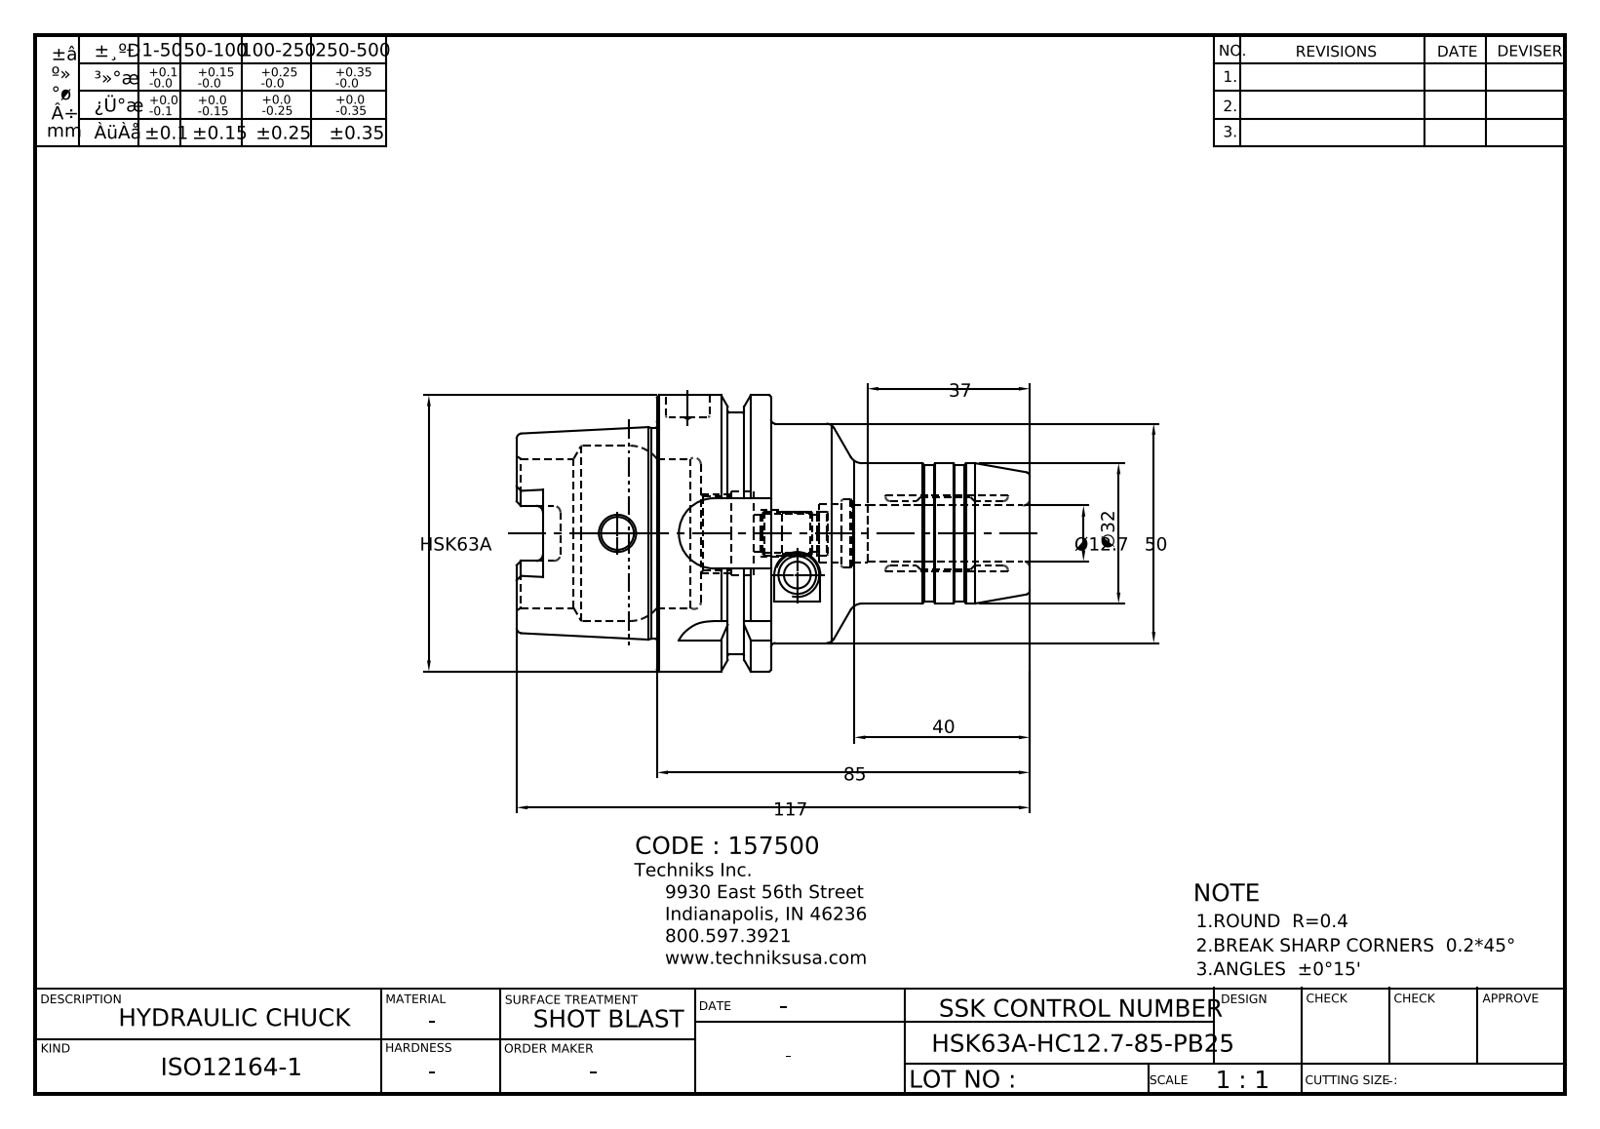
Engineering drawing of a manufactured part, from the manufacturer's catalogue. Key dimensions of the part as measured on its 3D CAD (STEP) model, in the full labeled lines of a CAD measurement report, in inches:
Part name (STEP PRODUCT): HSK63A-HC1_2-3_35-157500
STEP written by: PRO/ENGINEER BY PARAMETRIC TECHNOLOGY CORPORATION, 2015200 (CONFIG_CONTROL_DESIGN)
Units: inches
Bodies: 1 solid, 180 faces (63 planar, 49 cylindrical, 68 other)
Overall size (bounding box): 4.606 × 2.48 × 2.48
Volume: 8.63 in³ · Surface area: 47.16 in²
Round holes (diameter × count): ⌀0.295 ×1, ⌀0.394 ×1, ⌀0.433 ×1, ⌀0.5 ×1, ⌀0.669 ×1, ⌀0.709 ×1, ⌀0.748 ×1, ⌀1.339 ×1, ⌀1.575 ×1
Round bosses / shafts (diameter × count): ⌀2.48 ×1, ⌀2.165 ×1, ⌀1.969 ×1, ⌀1.891 ×1, ⌀1.26 ×1
Partial cylindrical surfaces — rounded edges, fillets, slot ends (radius × count): R0.059 ×6, R0.113 ×4, R0.315 ×4
Main face-to-face distances: 1.024, 0.394, 0.63, 0.866, 1.26, 0.241, 0.389, 1.654, 2.283, 4.606
Hole centre spacings: 1.657
